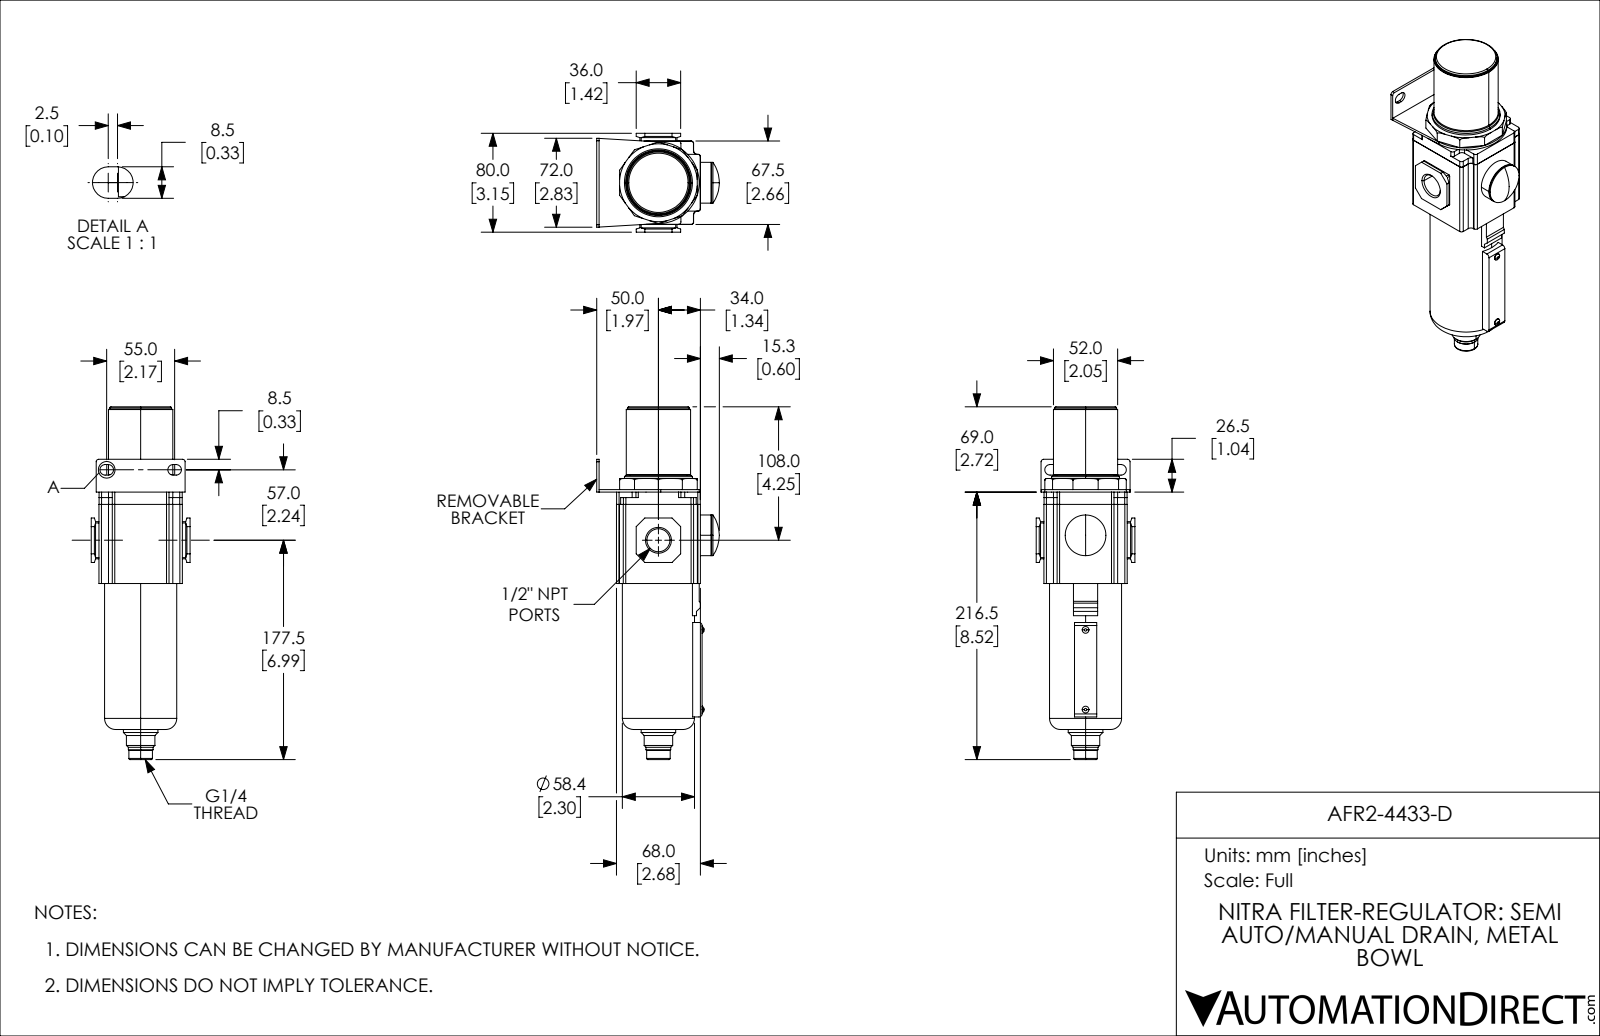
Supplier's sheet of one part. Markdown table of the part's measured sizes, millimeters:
| quantity | value |
| --- | --- |
| part name | AFR2-4433-D |
| STEP written by | SolidWorks 2019 (CONFIG_CONTROL_DESIGN) |
| units | millimeters |
| bodies | 1 solid, 237 faces (124 planar, 73 cylindrical, 40 other) |
| overall size | 285.5 × 99.28 × 80 |
| volume | 831 056 mm³ |
| surface area | 77 361 mm² |
| round holes (diameter × count) | 11.45 × 1, 18.63 × 1 |
| round bosses / shafts (diameter × count) | 5.5 × 2, 58.4 × 1, 55 × 1, 52 × 1, 50 × 1, 45.9 × 1, 33 × 1, 28 × 1 |
| partial cylindrical surfaces (radius × count) | 2 × 22, 3 × 12, 4.25 × 4, 2.5 × 2, 33 × 1 |
| main face-to-face distances | 2, 67.5, 67, 68, 16, 14, 69, 84, 76, 6.25 |
